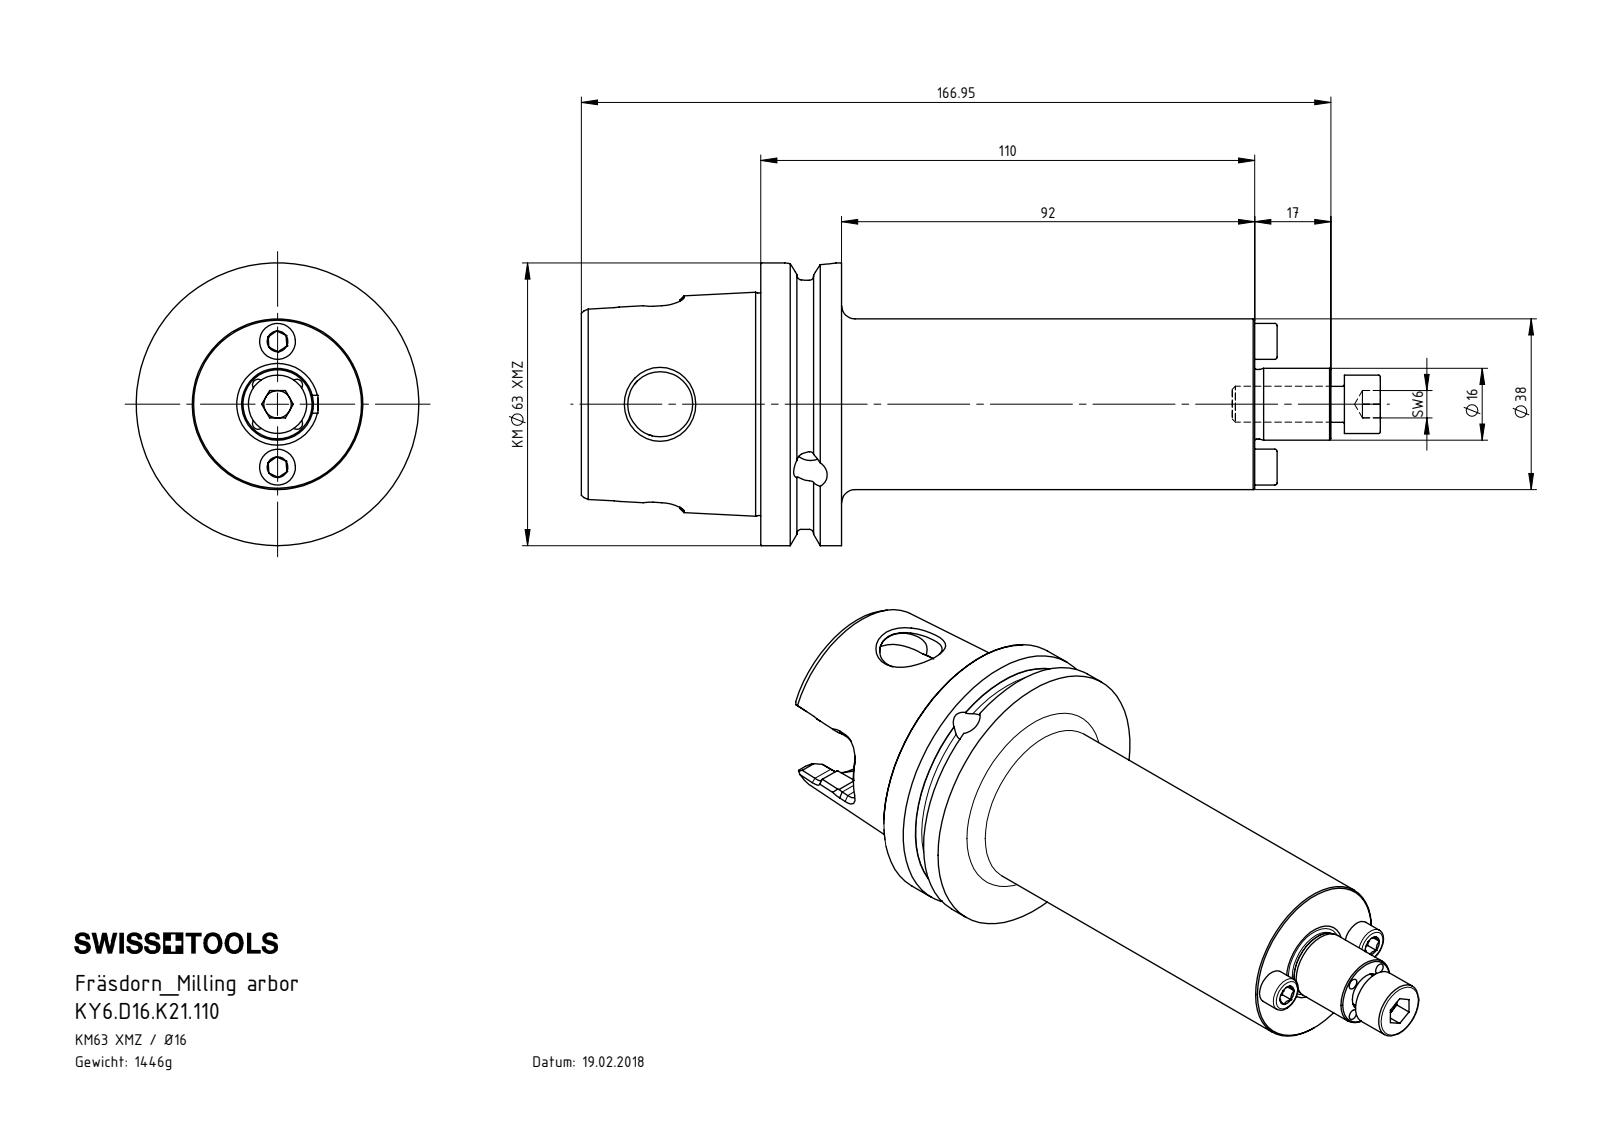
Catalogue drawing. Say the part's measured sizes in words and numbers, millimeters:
The part is named "D16-ER2.001.015_B; KY6-D16.K21.110_A; KY6.D16.K21.110; D16-ER1.002.025_A". Its 3-D file was written by "SolidWorks 2017 (CONFIG_CONTROL_DESIGN)". It is 4 solids with 392 faces: 87 planar, 100 cylindrical and 205 other. Overall it measures 177.95 by 62.95 by 62.95 millimeters. Its volume is 184 311 cubic millimeters and its surface area 37 143 square millimeters. Round holes: 3 of diameter 2.5, 2 of diameter 3.3, 2 of diameter 6, 2 of diameter 7.47, 1 of diameter 6.8, 1 of diameter 8.48, 1 of diameter 8.5, 1 of diameter 10, 1 of diameter 11.5, 1 of diameter 14.5, 1 of diameter 31.1, 1 of diameter 35.27. Round bosses or shafts: 3 of diameter 8, 2 of diameter 4, 2 of diameter 3, 1 of diameter 62.95, 1 of diameter 55.7, 1 of diameter 38, 1 of diameter 16, 1 of diameter 15.5. Partial cylindrical surfaces (rounded edges, fillets, slot ends): 6 of radius 4, 2 of radius 2, 2 of radius 7.04. The main face-to-face distances are 18, 110, 92, 19.1, 1.1, 111.1, 24, 6, 116, 4.9. The hole center spacings are 6.12, 10.6, 14, 18.83, 12.25, 28.
